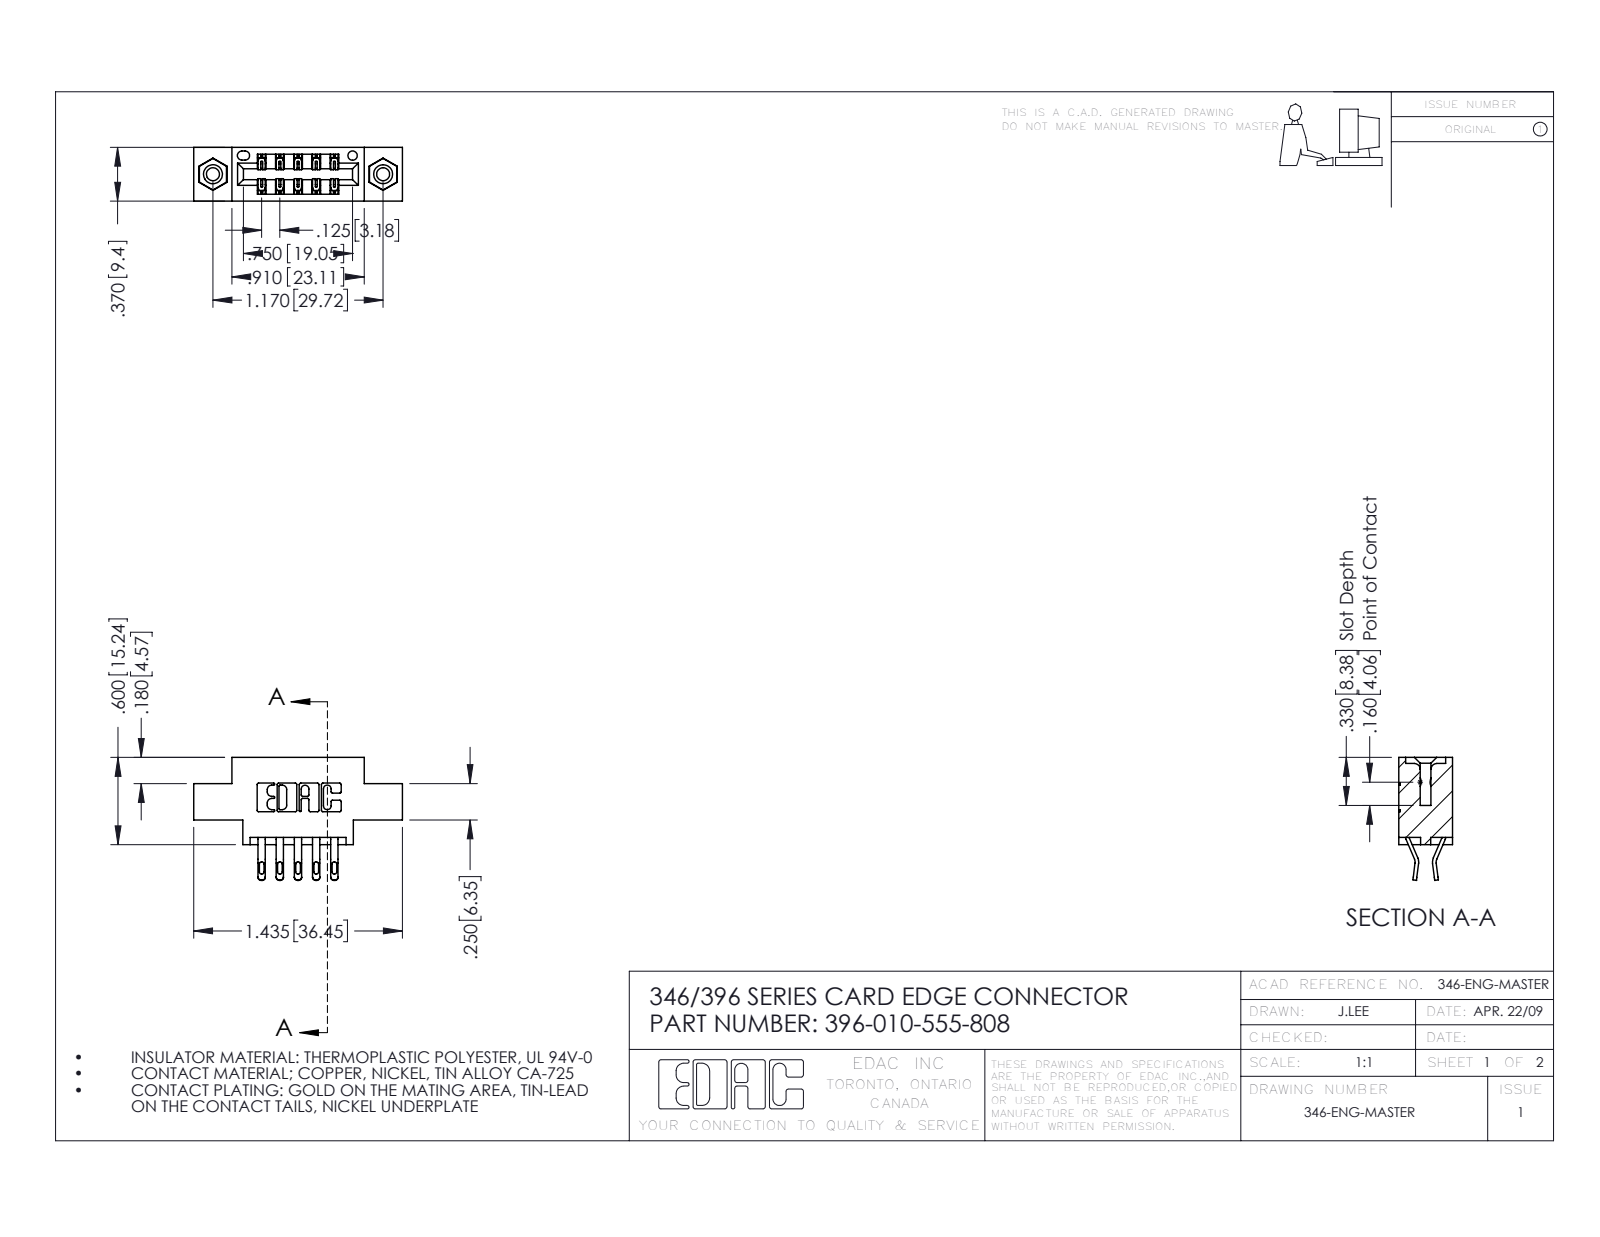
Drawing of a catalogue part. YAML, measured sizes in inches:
part_name: "346 Part_0.170 Offset - 0.156 Dia-TI; 345-250-001_345-250-003-102; 396-010-555-808; 345-292-001_555 Tail"
step_written_by: "SolidWorks 2016 (CONFIG_CONTROL_DESIGN)"
units: inches
bodies: {solids: 13, faces: 766, planar: 442, cylindrical: 308, other: 16}
overall_size: [1.435, 0.845, 0.37]
volume: 0.191
surface_area: 6.247
round_holes:
  - {diameter: 0.089, count: 2}
  - {diameter: 0.125, count: 2}
  - {diameter: 0.156, count: 2}
  - {diameter: 0.064, count: 1}
round_bosses_or_shafts:
  - {diameter: 0.155, count: 2}
partial_cylinders:
  - {radius: 0.01, count: 22}
  - {radius: 0.016, count: 20}
  - {radius: 0.02, count: 20}
  - {radius: 0.006, count: 15}
  - {radius: 0.007, count: 6}
  - {radius: 0.031, count: 6}
  - {radius: 0.026, count: 3}
  - {radius: 0.01, count: 2}
face_to_face_distances: [0.37, 0.25, 0.048, 0.322, 0.222, 0.148, 0.125, 0.1, 0.174, 0.025]
hole_center_spacings: [0.246, 0.969, 1.17]
